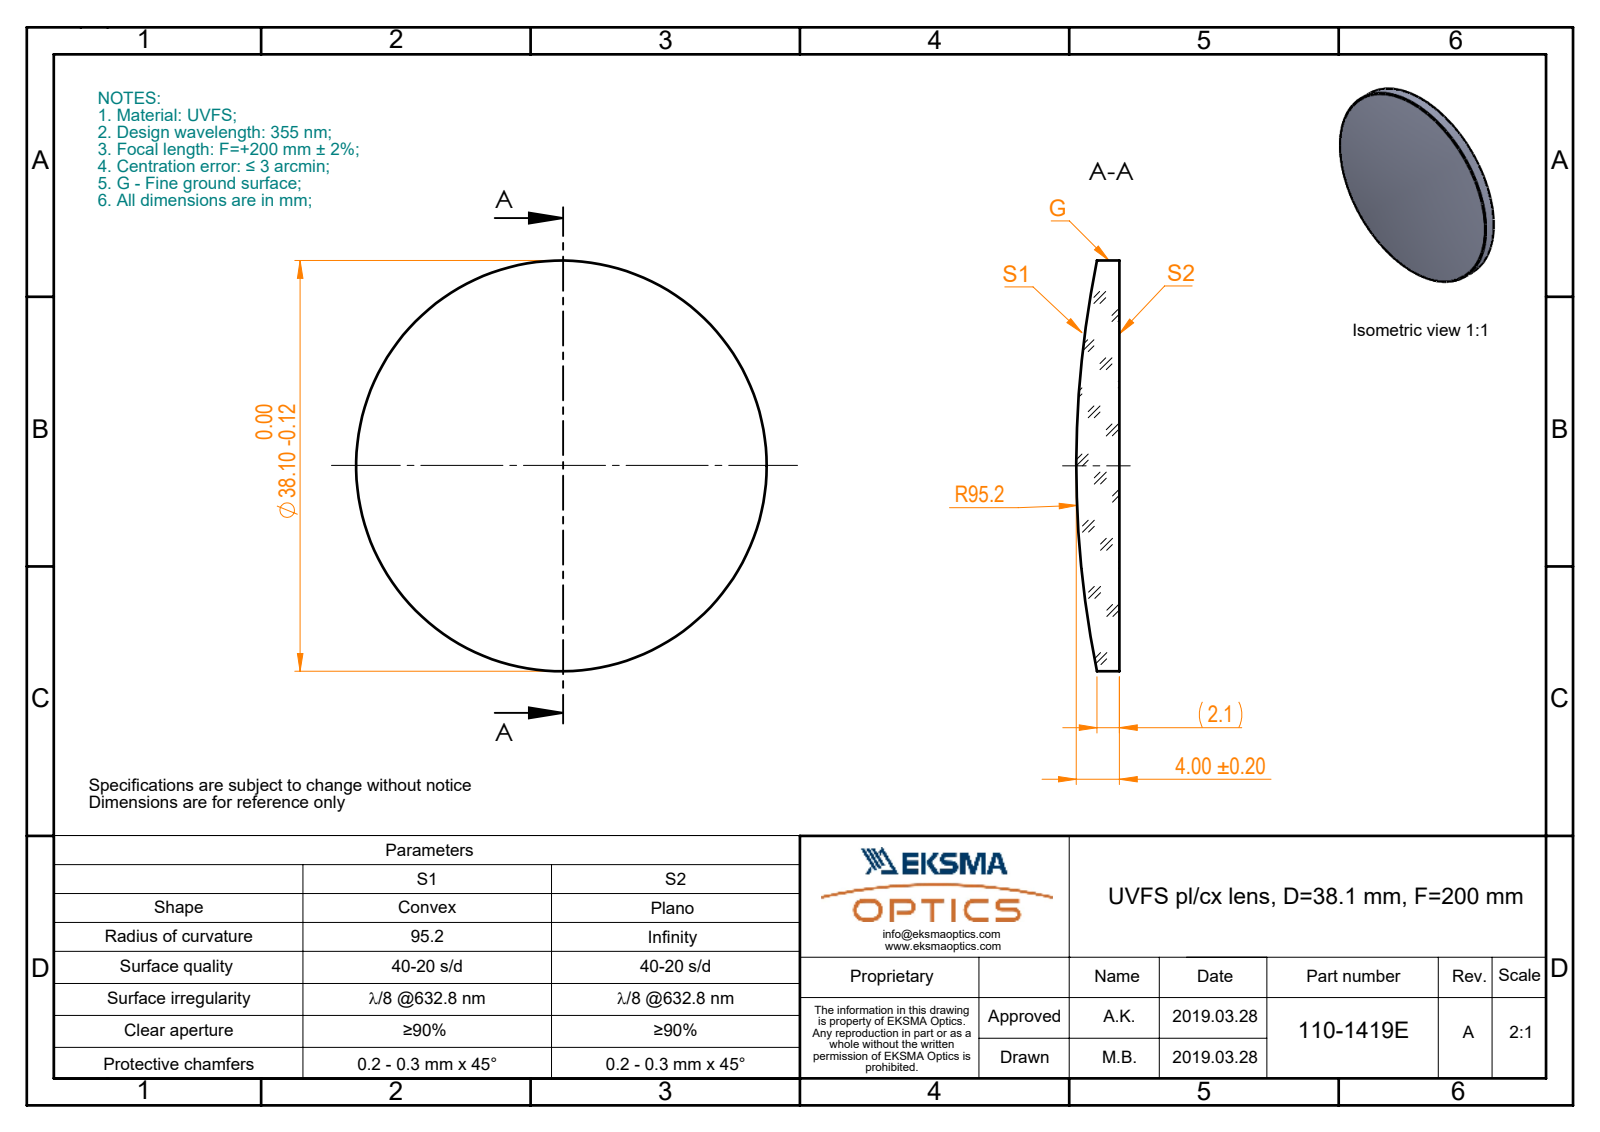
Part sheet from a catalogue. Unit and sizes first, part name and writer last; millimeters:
Units: millimetres
Overall size (bounding box): 38.1 × 38.1 × 4
Round bosses / shafts (diameter × count): ⌀38.1 ×1
Volume: 3 467 mm³ · Surface area: 2 540 mm²
Bodies: 1 solid, 5 faces (1 planar, 2 cylindrical, 2 other)
Part name (STEP PRODUCT): 110-1419E UVFS pl-cx 38.1 F200
STEP written by: SolidWorks 2017 (CONFIG_CONTROL_DESIGN)
